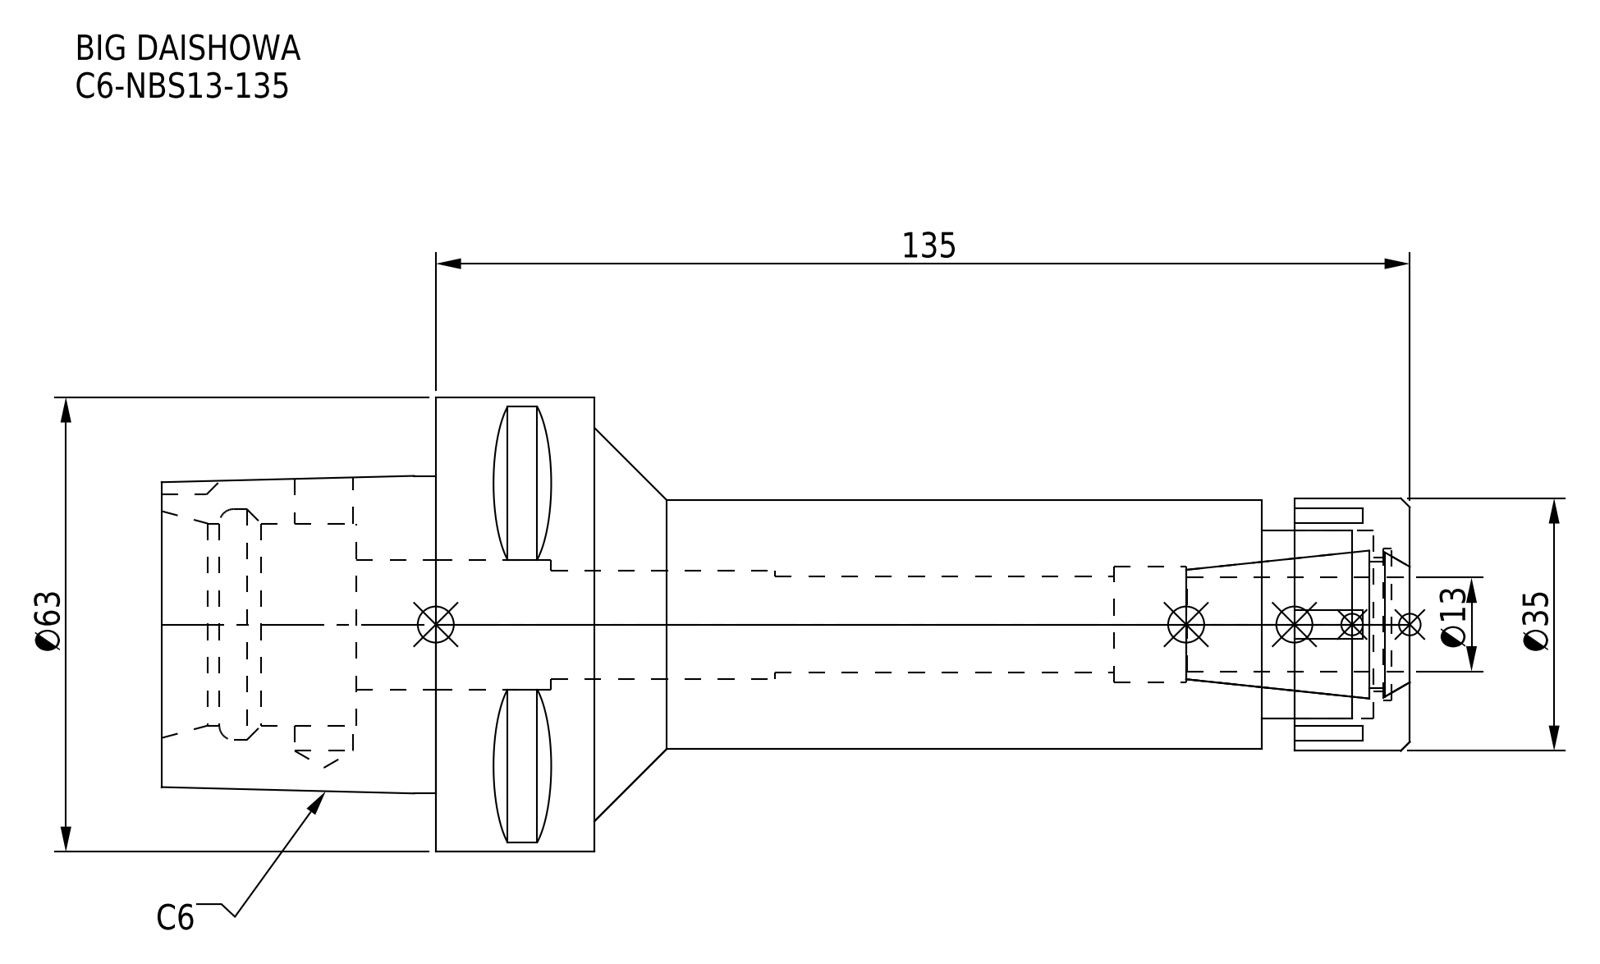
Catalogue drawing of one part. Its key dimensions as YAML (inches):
part_name: "C6-NBS13-135-130_ASM.stp; DXF_TEMP_ASSY_ASM_4_ASM.stp; C6-NBS13-135-FreeParts; C6-NBS13-135_1.stp (+3 more)"
step_written_by: "SolidWorks 2019 (CONFIG_CONTROL_DESIGN)"
units: inches
bodies: {solids: 2, faces: 112, planar: 61, cylindrical: 33, other: 18}
overall_size: [6.811, 2.48, 2.48]
volume: 11.23
surface_area: 62.43
round_holes:
  - {diameter: 0.319, count: 1}
  - {diameter: 0.524, count: 1}
  - {diameter: 0.591, count: 1}
  - {diameter: 0.63, count: 1}
  - {diameter: 0.709, count: 1}
  - {diameter: 0.728, count: 1}
  - {diameter: 0.827, count: 1}
  - {diameter: 1.024, count: 1}
  - {diameter: 1.102, count: 1}
  - {diameter: 1.26, count: 1}
round_bosses_or_shafts:
  - {diameter: 2.48, count: 1}
  - {diameter: 1.378, count: 1}
  - {diameter: 1.358, count: 1}
partial_cylinders:
  - {radius: 0.197, count: 1}
face_to_face_distances: [0.866, 4.449, 5.315, 0.433, 5.118, 6.811, 2.362, 1.496, 0.807, 0.63]
